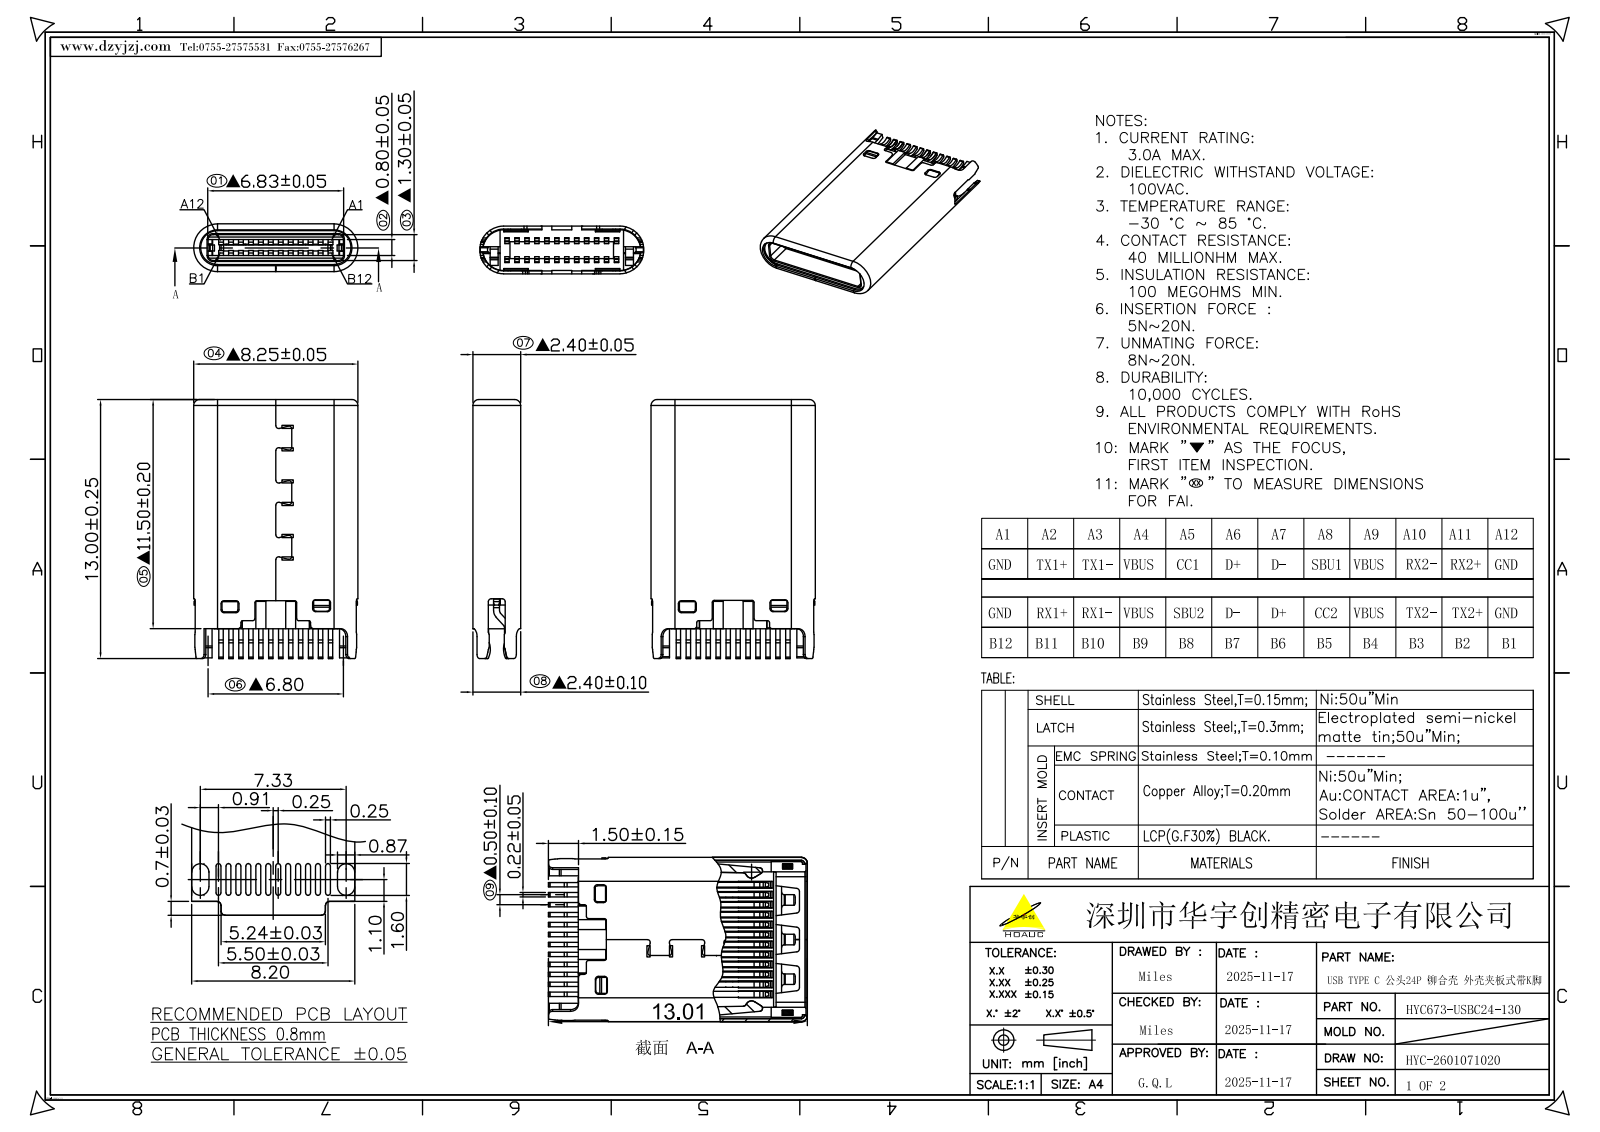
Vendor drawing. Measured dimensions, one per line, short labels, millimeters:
name: TANPIAN-PLASTIC_1_2__2_30_1_1
written by: CREO PARAMETRIC BY PTC INC, 2025010 (AUTOMOTIVE_DESIGN)
unit: mm
bodies: 1 solid, 928 faces (606 planar, 318 cylindrical, 4 other)
size: 13.01 × 8.25 × 2.42
volume: 173 mm³; area: 479 mm²
rounds: 47× R0.15, 39× R0.1, 12× R0.17, 8× R0.2, 6× R0.13, 6× R0.25, 6× R1.05, 4× R0.3
face distances: 2.4, 0.79, 0.8, 0.81, 1.61, 1.59, 1.05, 1.67, 0.62, 1.42
